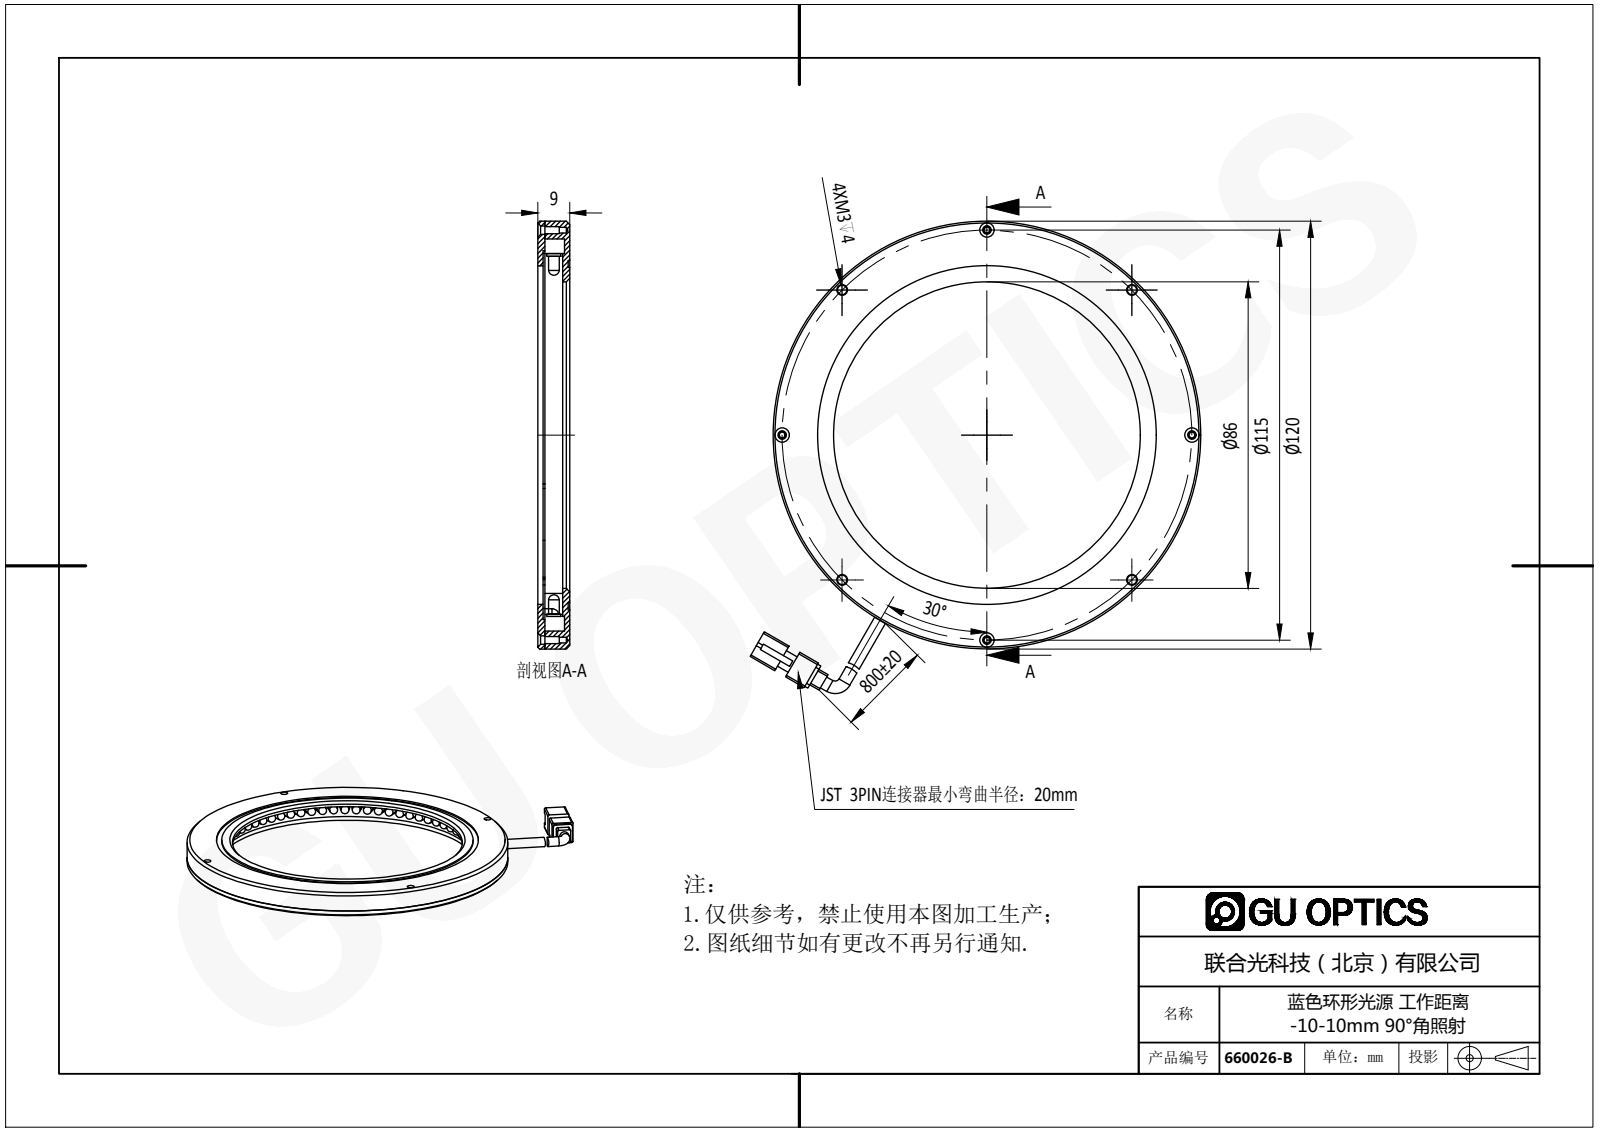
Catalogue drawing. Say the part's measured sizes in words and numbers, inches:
The part is named "660026-B". Its 3-D file was written by "SolidWorks 2016 (AUTOMOTIVE_DESIGN)". It is 75 solids with 1433 faces: 928 planar, 409 cylindrical and 96 other. Overall it measures 5.218 by 4.978 by 0.437 inches. Its volume is 1.874 cubic inches and its surface area 59.39 square inches. Round holes: 4 of diameter 0.063, 4 of diameter 0.079, 4 of diameter 0.094, 4 of diameter 0.102, 4 of diameter 0.118, 1 of diameter 0.138, 1 of diameter 3.386, 1 of diameter 3.74, 1 of diameter 3.858, 1 of diameter 4.055, 1 of diameter 4.075, 1 of diameter 4.331. Round bosses or shafts: 69 of diameter 0.15, 69 of diameter 0.118, 2 of diameter 0.138, 1 of diameter 4.724, 1 of diameter 4.079, 1 of diameter 4.008, 1 of diameter 3.701. Partial cylindrical surfaces (rounded edges, fillets, slot ends): 12 of radius 0.039, 8 of radius 0.02, 2 of radius 0.081, 1 of radius 0.071, 1 of radius 0.295, 1 of radius 2.024, 1 of radius 2.126. The main face-to-face distances are 0.276, 0.079, 0.354, 0.02, 0.059, 0.217, 0.295, 0.197, 0.236, 0.039. The hole center spacings are 1.733, 2.264, 3.202, 4.183, 4.183, 4.528, 1.732, 2.263.
